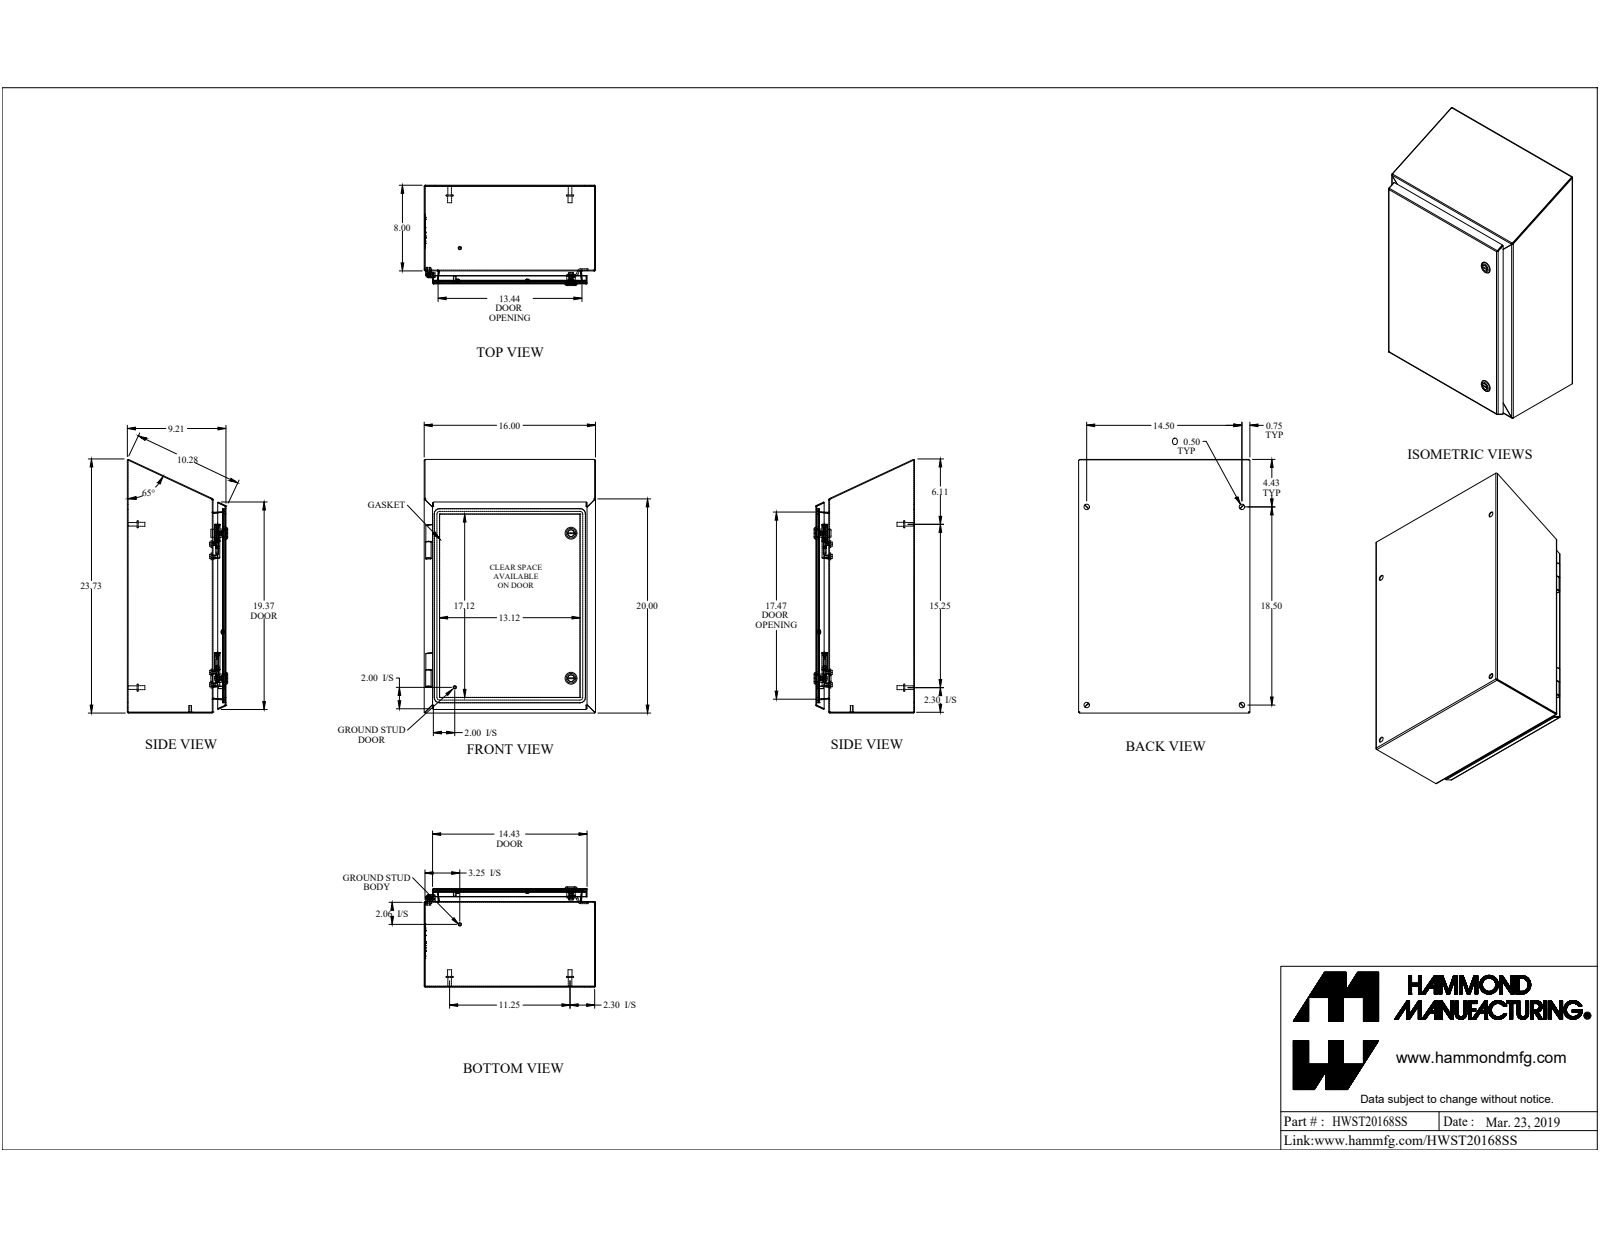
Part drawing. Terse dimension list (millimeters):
name: HWST20168S16
written by: SolidWorks 2019 (AUTOMOTIVE_DESIGN)
unit: mm
bodies: 43 solids, 1055 faces (649 planar, 292 cylindrical, 114 other)
size: 601.6 × 406.4 × 238
volume: 1 975 000 mm³; area: 2 093 000 mm²
holes: 8× ⌀4.9, 6× ⌀12.7, 4× ⌀6.1, 4× ⌀7, 2× ⌀3.3, 2× ⌀5, 2× ⌀9.8, 2× ⌀16, 2× ⌀19.5, 1× ⌀6.1, 1× ⌀88.9
bosses: 8× ⌀5.7, 6× ⌀15.9, 4× ⌀16.5, 4× ⌀9.5, 4× ⌀8.4, 4× ⌀6.4, 3× ⌀6, 2× ⌀27.9
rounds: 24× R6.4, 16× R1, 16× R2.7, 12× R0.3, 12× R0.9, 12× R3.2, 9× R2.7, 7× R0.9
face distances: 1.8, 404.6, 230.3, 232.1, 1.8, 232.1, 233.9, 402.7, 406.4, 201.4
hole spacings: 29, 304.3, 275.3, 304.3, 333.2, 368.3, 469.9, 597.1
